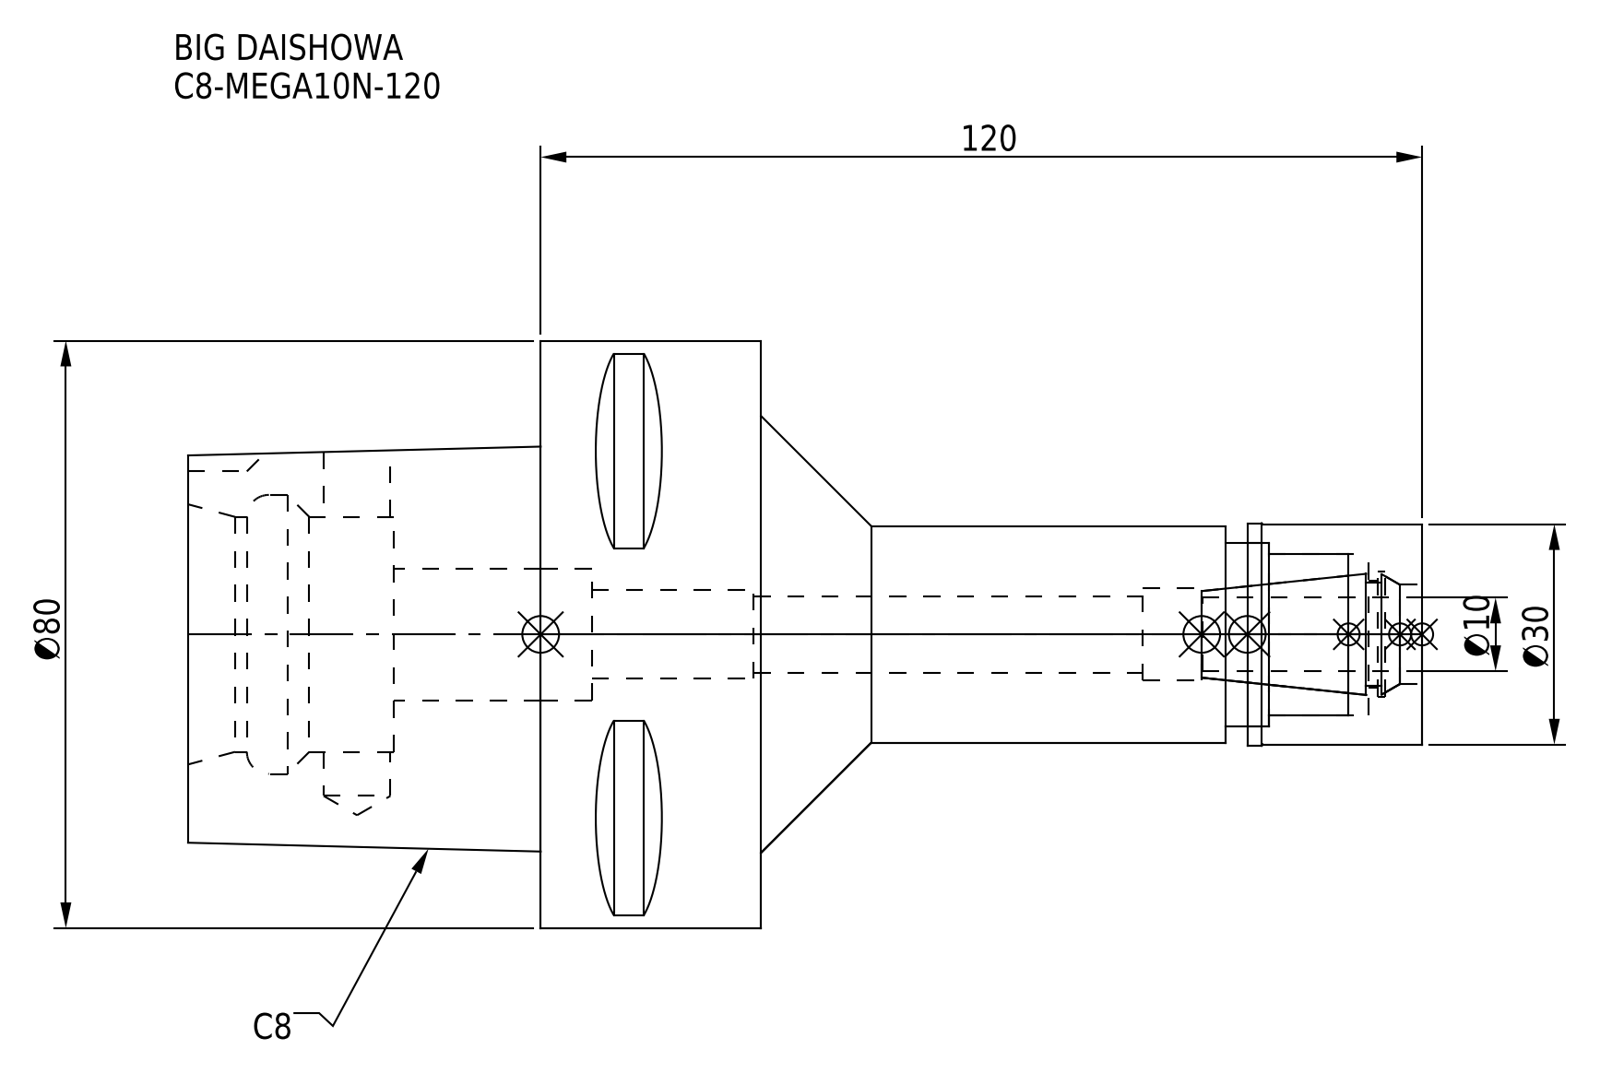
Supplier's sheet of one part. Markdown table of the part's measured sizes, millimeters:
| quantity | value |
| --- | --- |
| part name | C8-MEGA10N-120_1.stp; MGN10_1.stp; C8-MEGA10N-120; C8-MEGA10N-120-100.stp (+3 more) |
| STEP written by | SolidWorks 2019 (CONFIG_CONTROL_DESIGN) |
| units | millimeters |
| bodies | 2 solids, 98 faces (39 planar, 41 cylindrical, 18 other) |
| overall size | 168 × 80 × 80 |
| volume | 285 385 mm³ |
| surface area | 46 080 mm² |
| round holes (diameter × count) | 9.1 × 1, 10.4 × 1, 12 × 1, 12.5 × 1, 13.5 × 1, 14.5 × 1, 17 × 1, 18 × 1, 22 × 1, 25 × 1, 32 × 1, 38 × 1 |
| round bosses / shafts (diameter × count) | 80 × 1, 30.3 × 1, 30 × 1, 29.5 × 1 |
| partial cylindrical surfaces (radius × count) | 6 × 1 |
| main face-to-face distances | 30, 78, 48, 28, 20, 90, 120, 168, 140, 50 |
